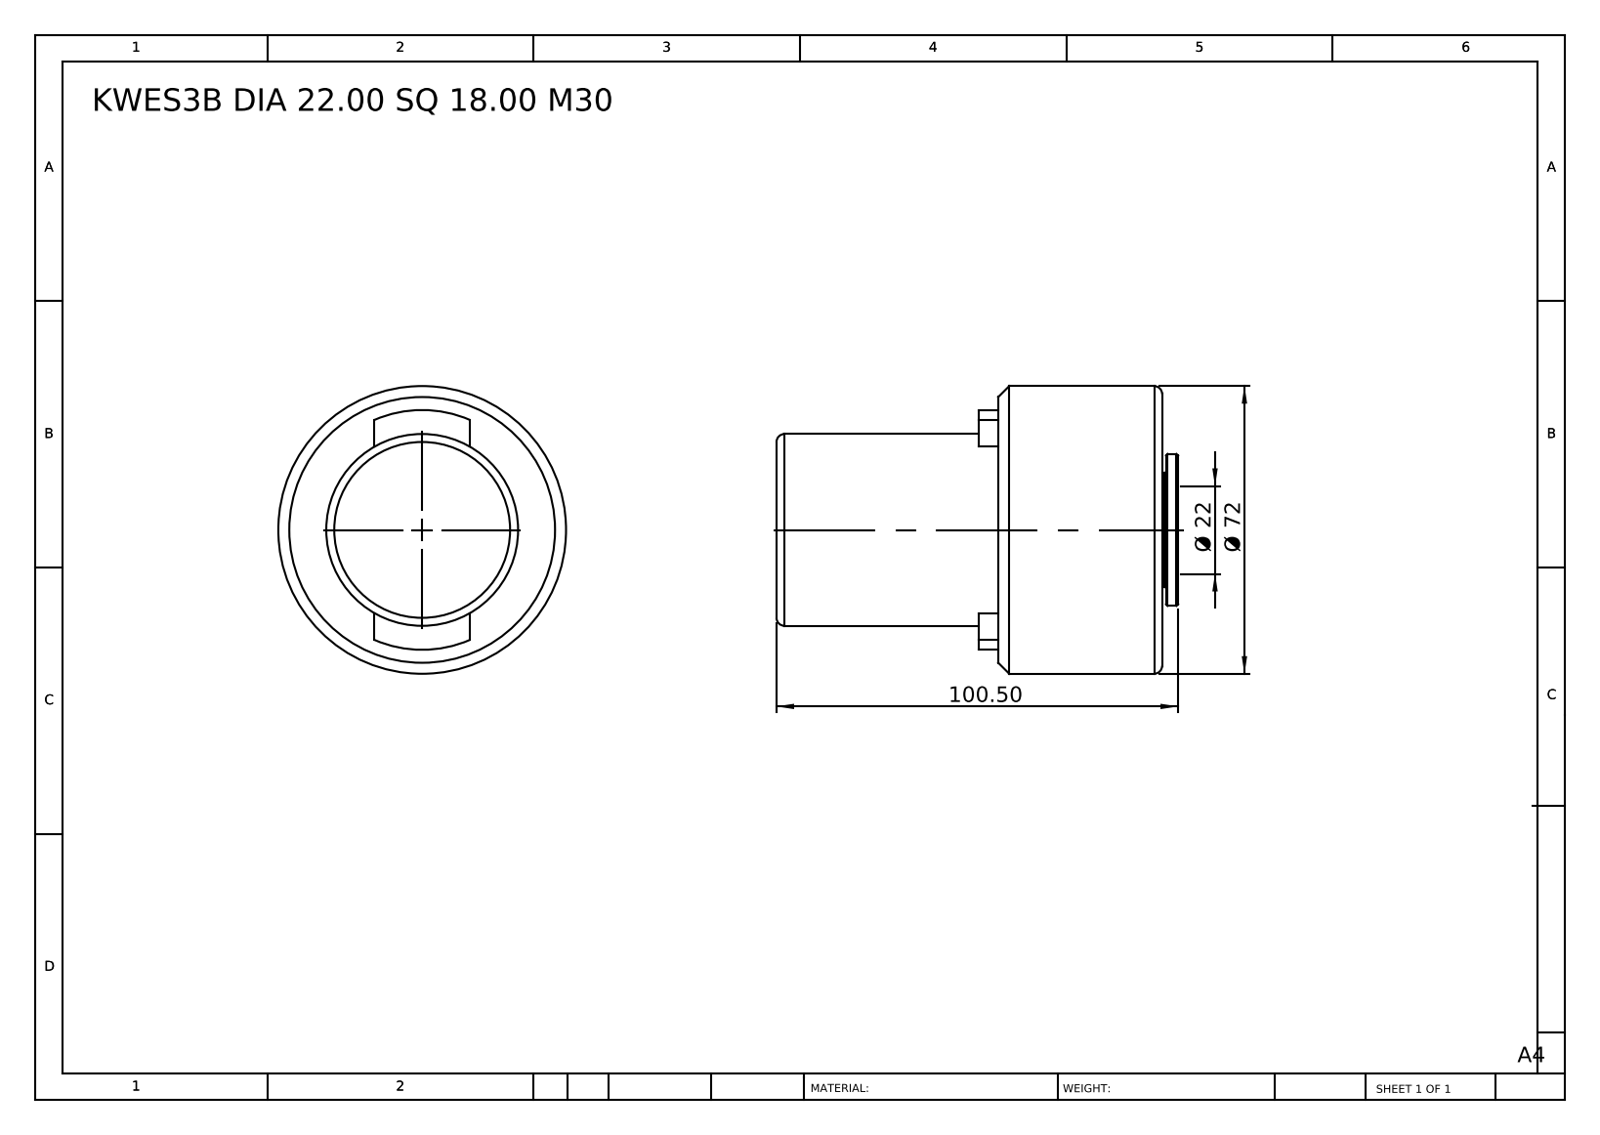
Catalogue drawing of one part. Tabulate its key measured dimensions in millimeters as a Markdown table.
| quantity | value |
| --- | --- |
| part name | KWES3B DIA 22.00 SQ 18.00 M30 |
| STEP written by | SolidWorks 2014 (CONFIG_CONTROL_DESIGN) |
| units | millimeters |
| bodies | 1 solid, 39 faces (12 planar, 13 cylindrical, 14 other) |
| overall size | 100.5 × 72 × 72 |
| volume | 256 508 mm³ |
| surface area | 29 328 mm² |
| round holes (diameter × count) | 22 × 1 |
| round bosses / shafts (diameter × count) | 72 × 1, 48 × 1, 38 × 1, 28.5 × 1 |
| partial cylindrical surfaces (radius × count) | 30 × 1 |
| main face-to-face distances | 96.5, 55.5, 41, 5, 100.5, 45, 4, 97.5, 42, 1 |
